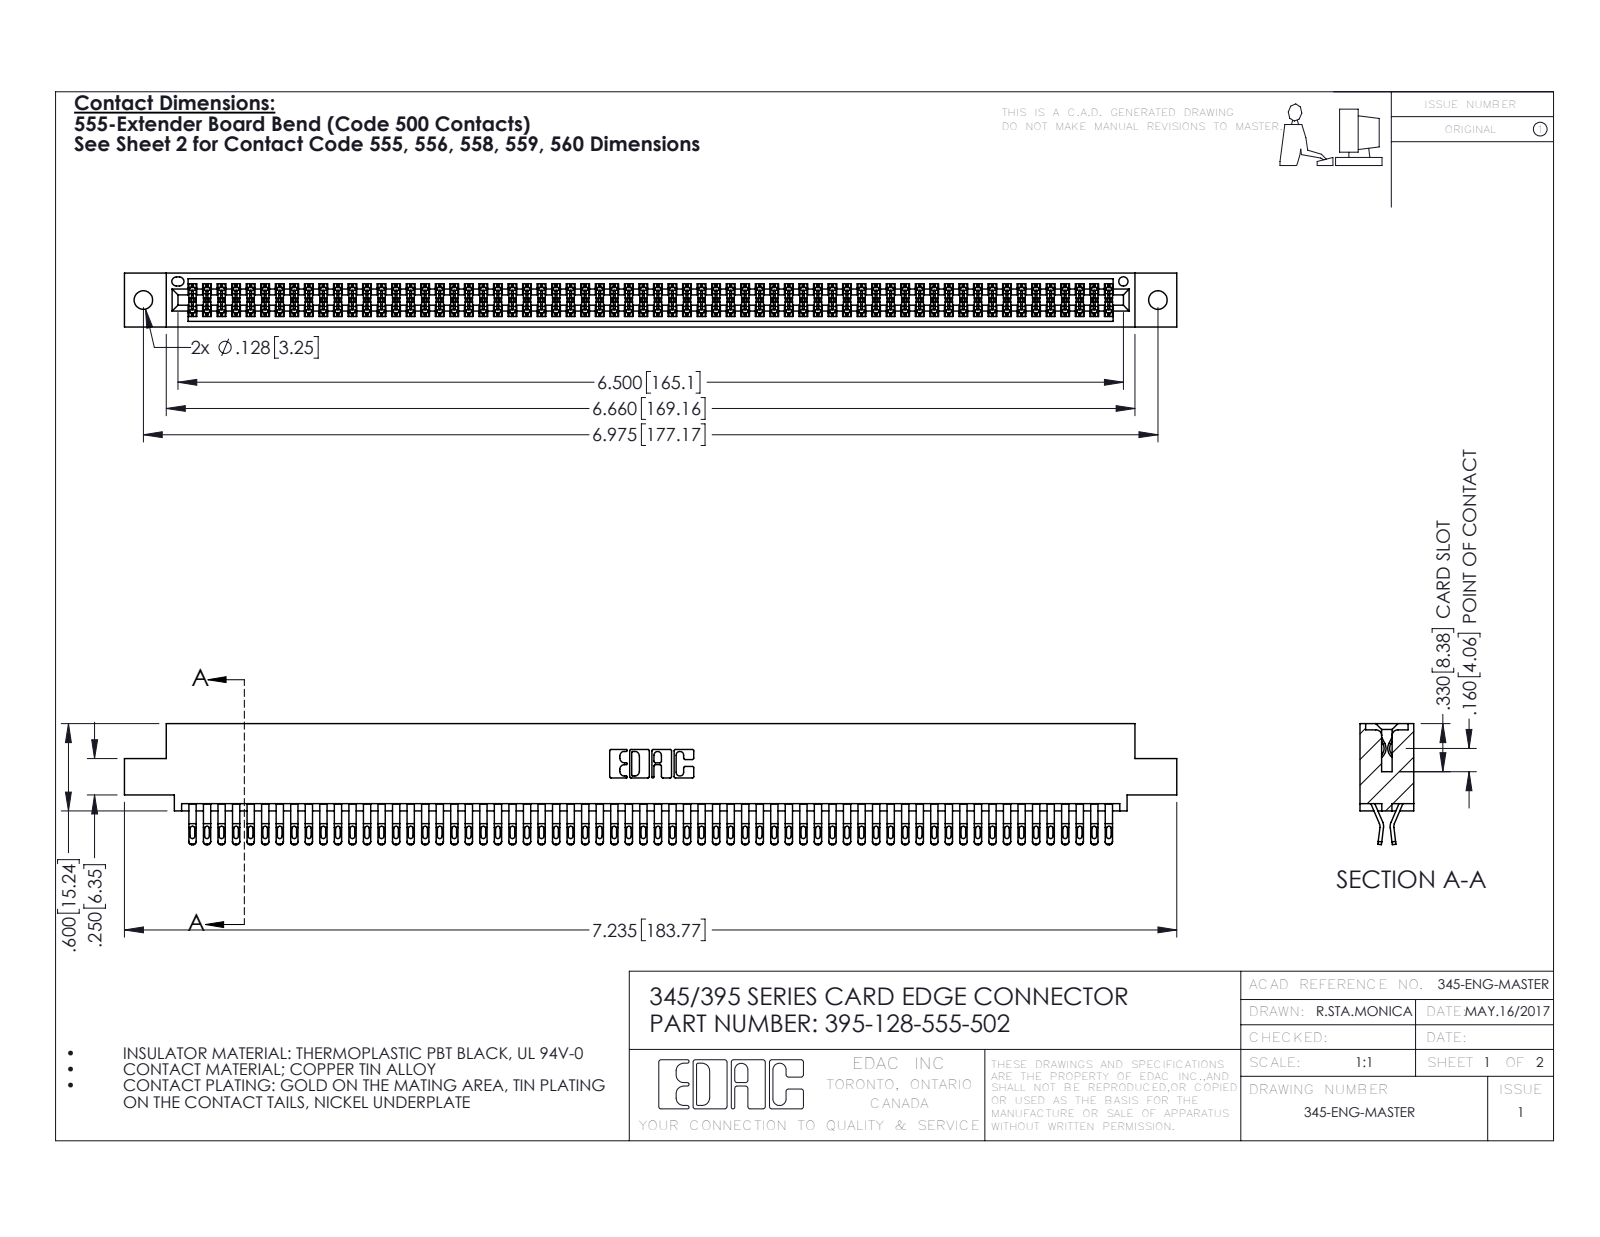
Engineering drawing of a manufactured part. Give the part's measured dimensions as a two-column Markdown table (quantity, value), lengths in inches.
| quantity | value |
| --- | --- |
| part name | 395-128-555-502; 345-292-001_555 Tail; 345 Part_0.110 Offset - 0.128 Dia |
| STEP written by | SolidWorks 2016 (CONFIG_CONTROL_DESIGN) |
| units | inches |
| bodies | 129 solids, 7298 faces (4052 planar, 3246 cylindrical, 0 other) |
| overall size | 7.235 × 0.832 × 0.37 |
| volume | 1.118 in³ |
| surface area | 44.35 in² |
| round holes (diameter × count) | 0.128 × 2, 0.064 × 1 |
| partial cylindrical surfaces (radius × count) | 0.016 × 320, 0.02 × 256, 0.006 × 192, 0.01 × 22, 0.007 × 6, 0.031 × 6, 0.026 × 3, 0.01 × 2 |
| main face-to-face distances | 0.298, 0.072, 0.025, 0.37, 0.2, 0.098, 0.272, 0.225, 0.175, 0.149 |
| hole center spacings | 0.27, 6.739, 6.975 |
